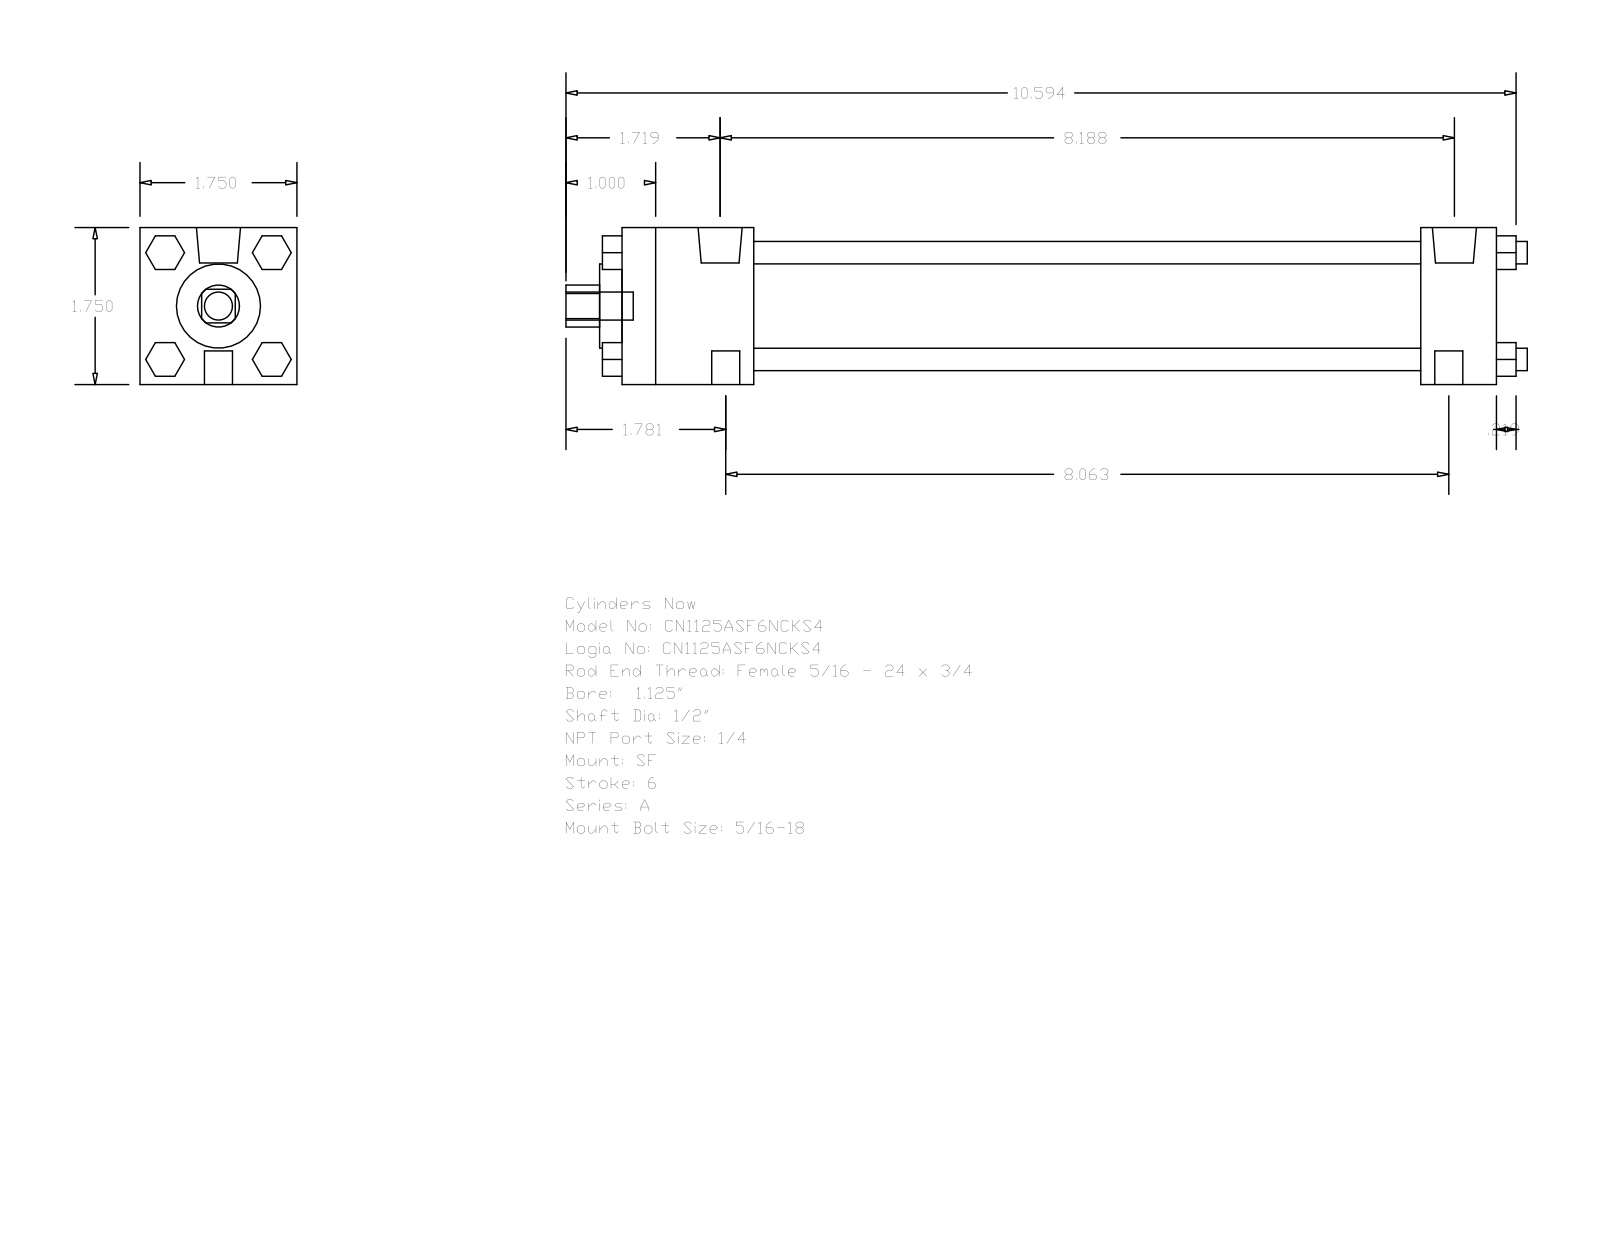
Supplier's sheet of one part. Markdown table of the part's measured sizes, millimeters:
| quantity | value |
| --- | --- |
| part name | A_SF__0112_0.5 |
| STEP written by | GSSL Pune (CONFIG_CONTROL_DESIGN) |
| units | millimeters |
| bodies | 0 solids, 120 faces (92 planar, 28 cylindrical, 0 other) |
| overall size | 272.26 × 44.45 × 44.45 |
| round holes (diameter × count) | 12.7 × 1, 23.81 × 1, 31.88 × 1 |
| round bosses / shafts (diameter × count) | 6.35 × 4, 7.94 × 3, 12.49 × 2, 5.56 × 2 |
| partial cylindrical surfaces (radius × count) | 5.94 × 1 |
| main face-to-face distances | 44.46, 247.64, 226.21, 21.43, 37.3, 188.91, 210.34, 9.53, 5.59, 9.52 |
